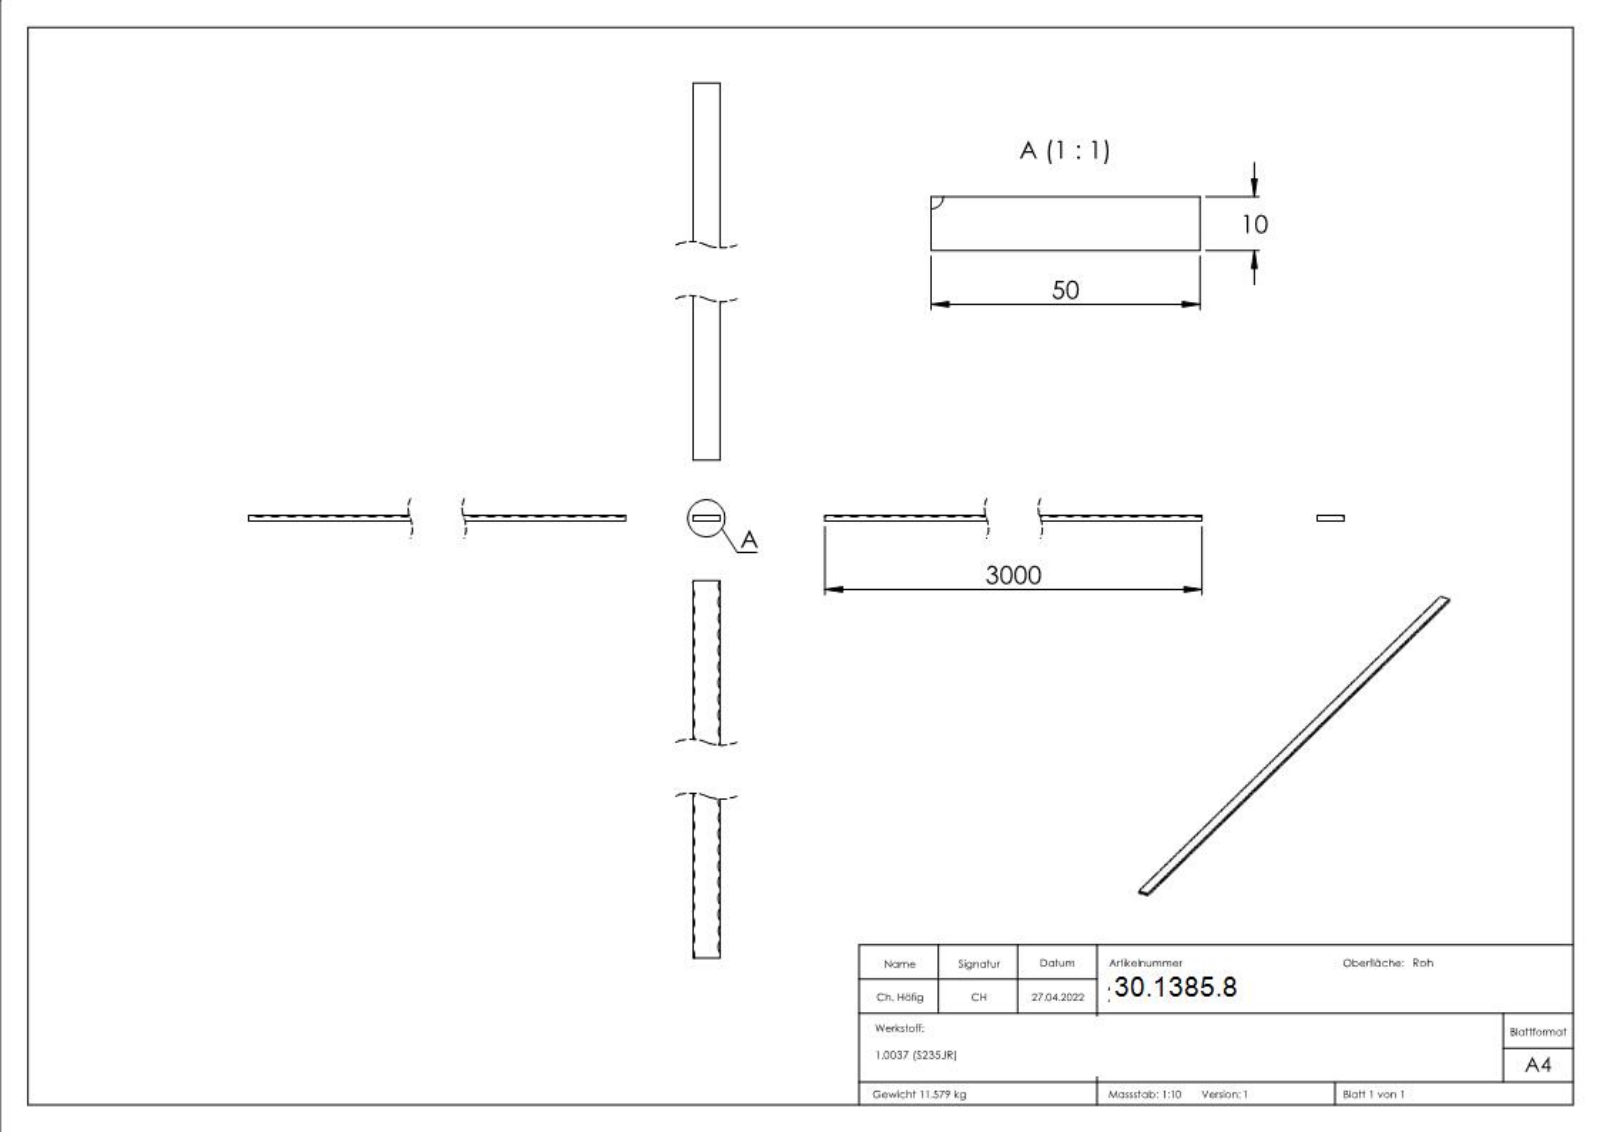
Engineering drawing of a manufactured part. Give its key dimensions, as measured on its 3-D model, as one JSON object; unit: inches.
{"part_name": "2006-50", "step_written_by": "SolidWorks 2018 (CONFIG_CONTROL_DESIGN)", "units": "inches", "bodies": {"solids": 1, "faces": 443, "planar": 124, "cylindrical": 0, "other": 319}, "overall_size": [118.11, 1.969, 0.394], "volume_in3": 90.62, "surface_area_in2": 554.8, "face_to_face_distances": [0.394, 1.969, 118.11, 0.39, 0.144, 0.129, 0.013, 59.055, 0.944, 1.024]}
